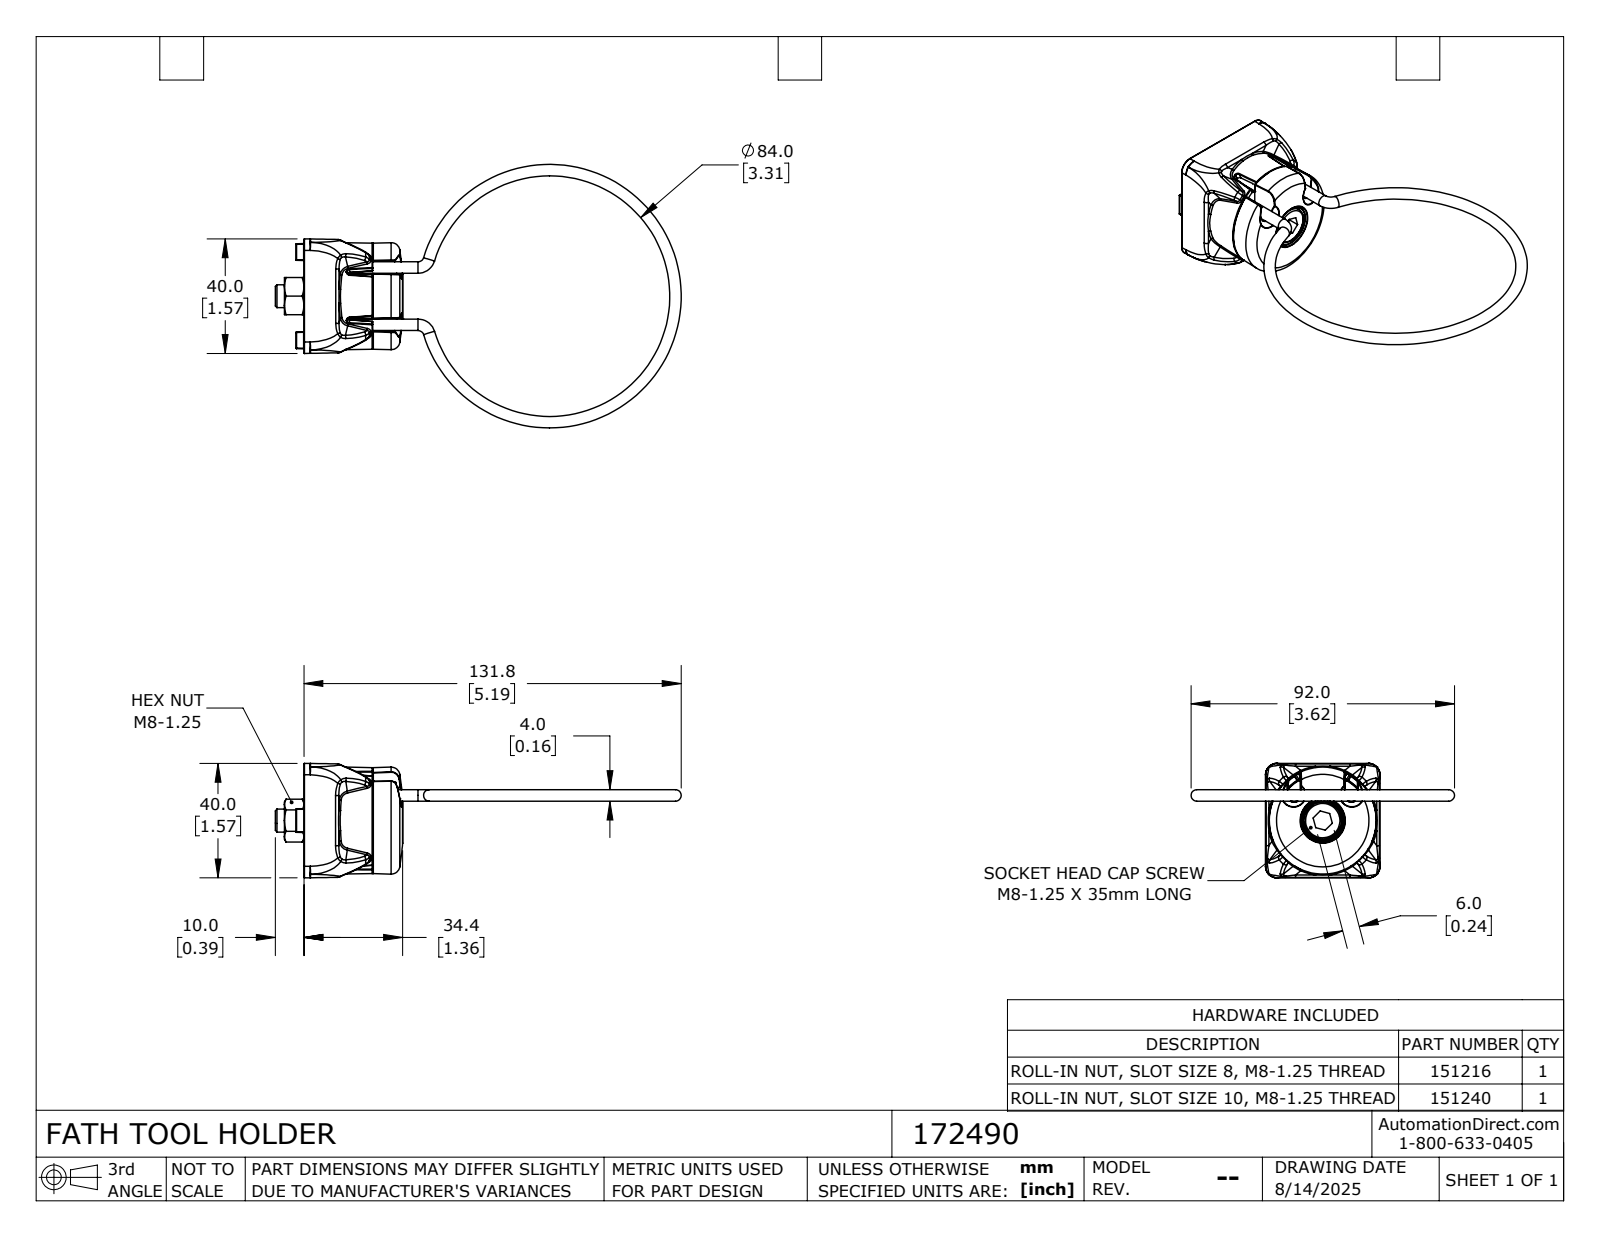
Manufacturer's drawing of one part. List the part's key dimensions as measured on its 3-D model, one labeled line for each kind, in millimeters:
Part name (STEP PRODUCT): 172490
STEP written by: SolidWorks 2024 (CONFIG_CONTROL_DESIGN)
Units: millimetres
Bodies: 7 solids, 1239 faces (222 planar, 296 cylindrical, 721 other)
Overall size (bounding box): 141.76 × 92 × 40
Volume: 42 287 mm³ · Surface area: 23 535 mm²
Round holes (diameter × count): ⌀6.8 ×1, ⌀8 ×1, ⌀13.01 ×1
Round bosses / shafts (diameter × count): ⌀4 ×6, ⌀13 ×1
Partial cylindrical surfaces — rounded edges, fillets, slot ends (radius × count): R0.2 ×142, R0.5 ×22, R1 ×8, R4 ×8, R1.2 ×4, R2.15 ×2, R16.5 ×1
Main face-to-face distances: 13.5, 30.8, 8, 6, 13.3, 10.7, 17, 10.5, 24, 9.2
